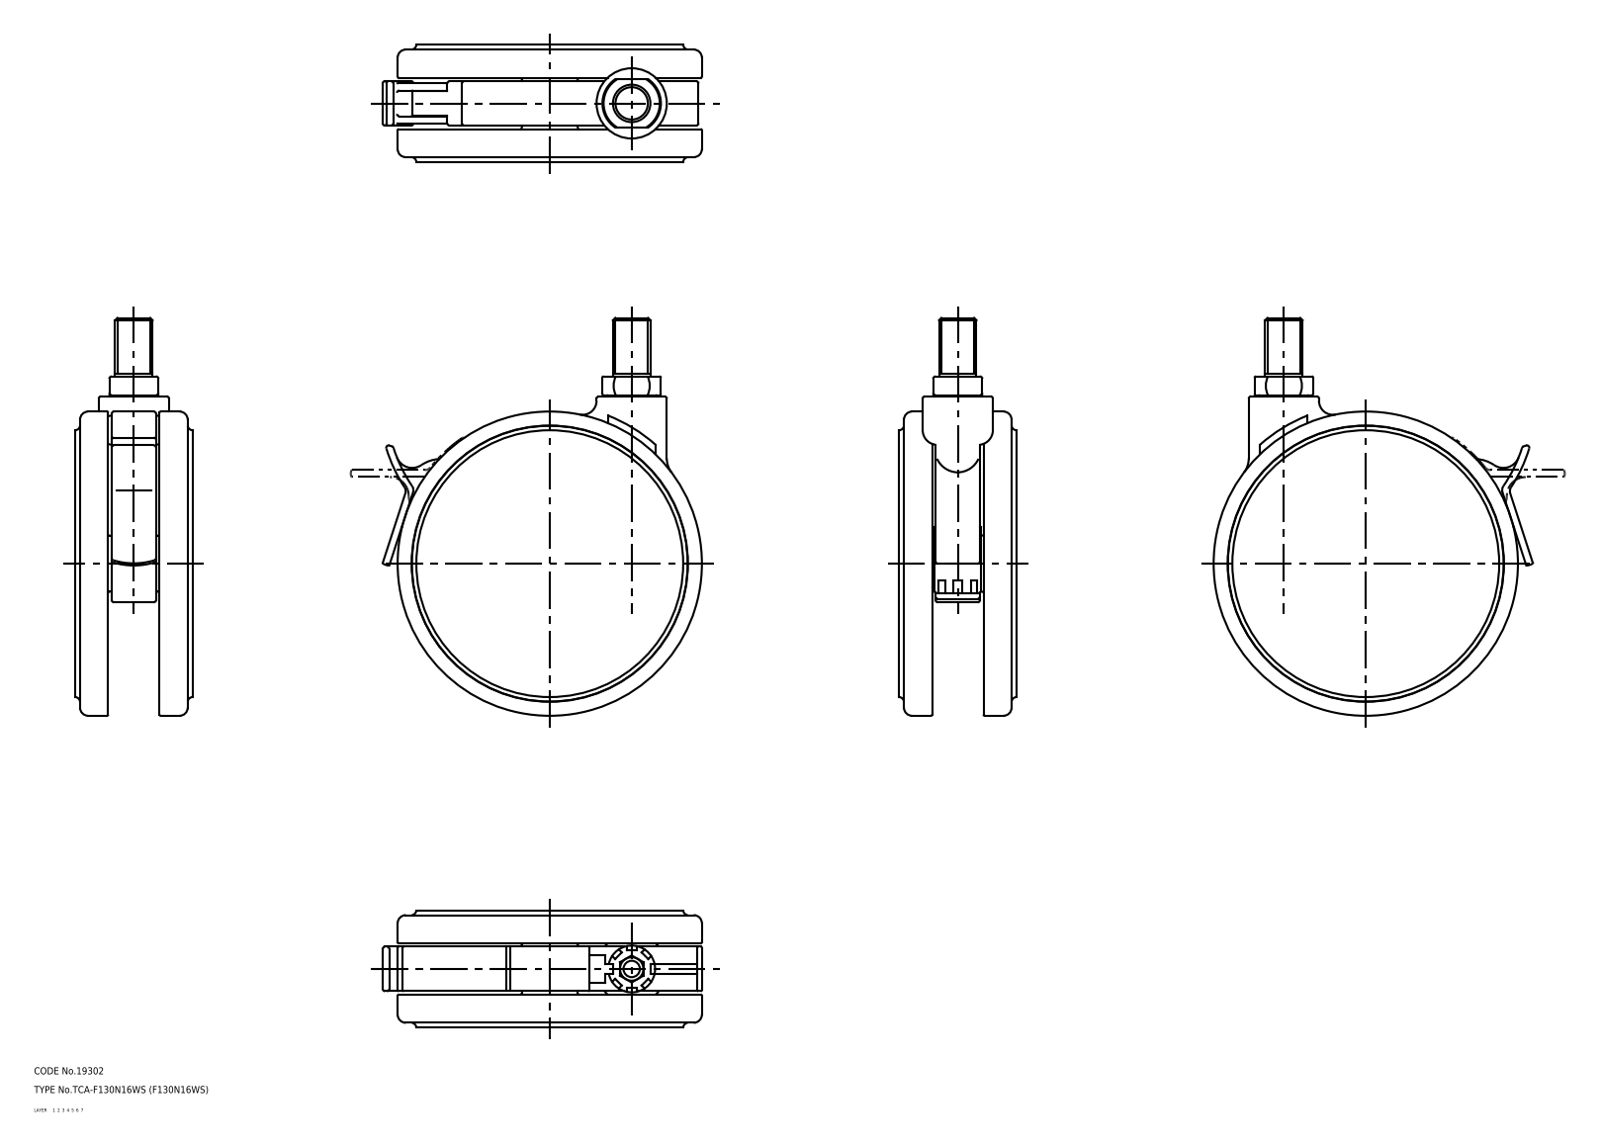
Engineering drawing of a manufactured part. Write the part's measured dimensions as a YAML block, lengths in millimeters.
part_name: "67124458; 67124471; 67124484; 67124497 (+1 more)"
step_written_by: "CADfix (AUTOMOTIVE_DESIGN)"
units: millimeters
bodies: {solids: 5, faces: 276, planar: 0, cylindrical: 0, other: 276}
overall_size: [170, 136.44, 50]
volume: 466052
surface_area: 103443
